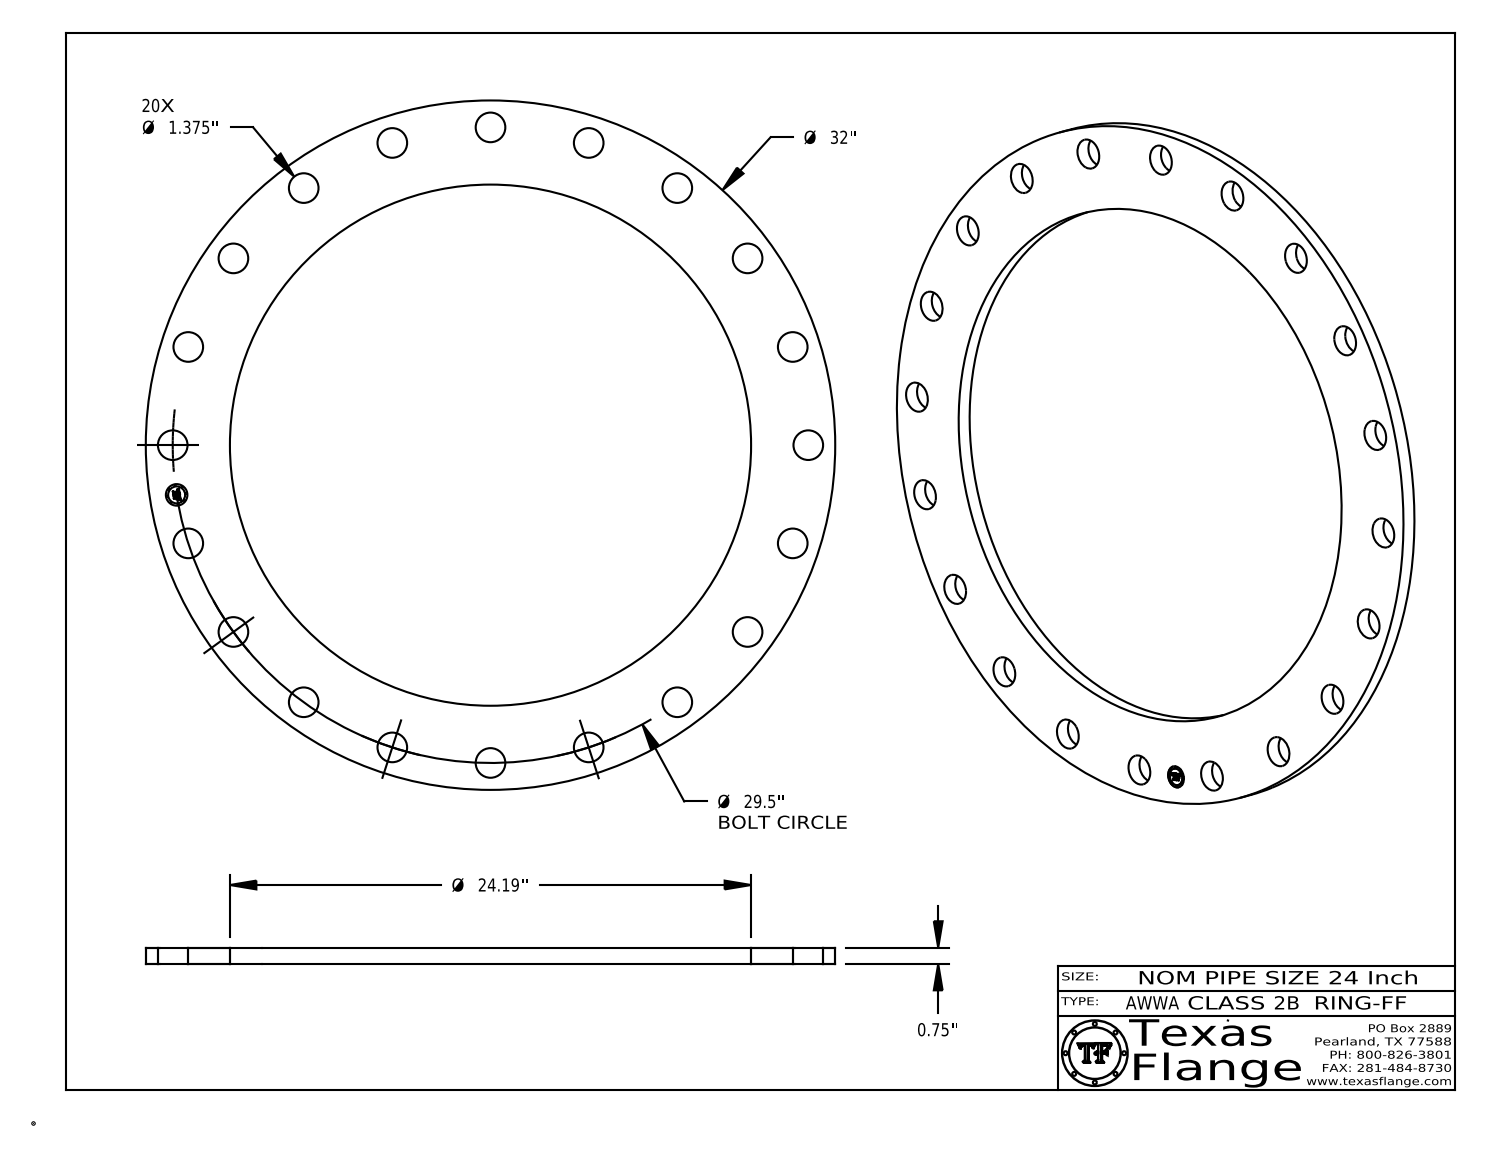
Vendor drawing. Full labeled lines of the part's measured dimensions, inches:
Part name (STEP PRODUCT): AWWA Class 2B-RING-FF
STEP written by: CATIA V5 STEP AP214 (AUTOMOTIVE_DESIGN)
Units: inches
Bodies: 1 solid, 431 faces (367 planar, 64 cylindrical, 0 other)
Overall size (bounding box): 32 × 32 × 0.75
Volume: 236.2 in³ · Surface area: 827.3 in²
Round holes (diameter × count): ⌀1.375 ×20, ⌀1 ×1, ⌀24.19 ×1
Round bosses / shafts (diameter × count): ⌀0.061 ×8, ⌀32 ×1, ⌀0.788 ×1
Main face-to-face distances: 0.75, 0.735, 0.015, 0.298, 0.293, 0.054, 0.193, 0.248, 0.044, 0.15
Hole centre spacings: 14.75, 29.137, 4.615, 17.34, 20.859, 23.866, 26.285, 9.116
